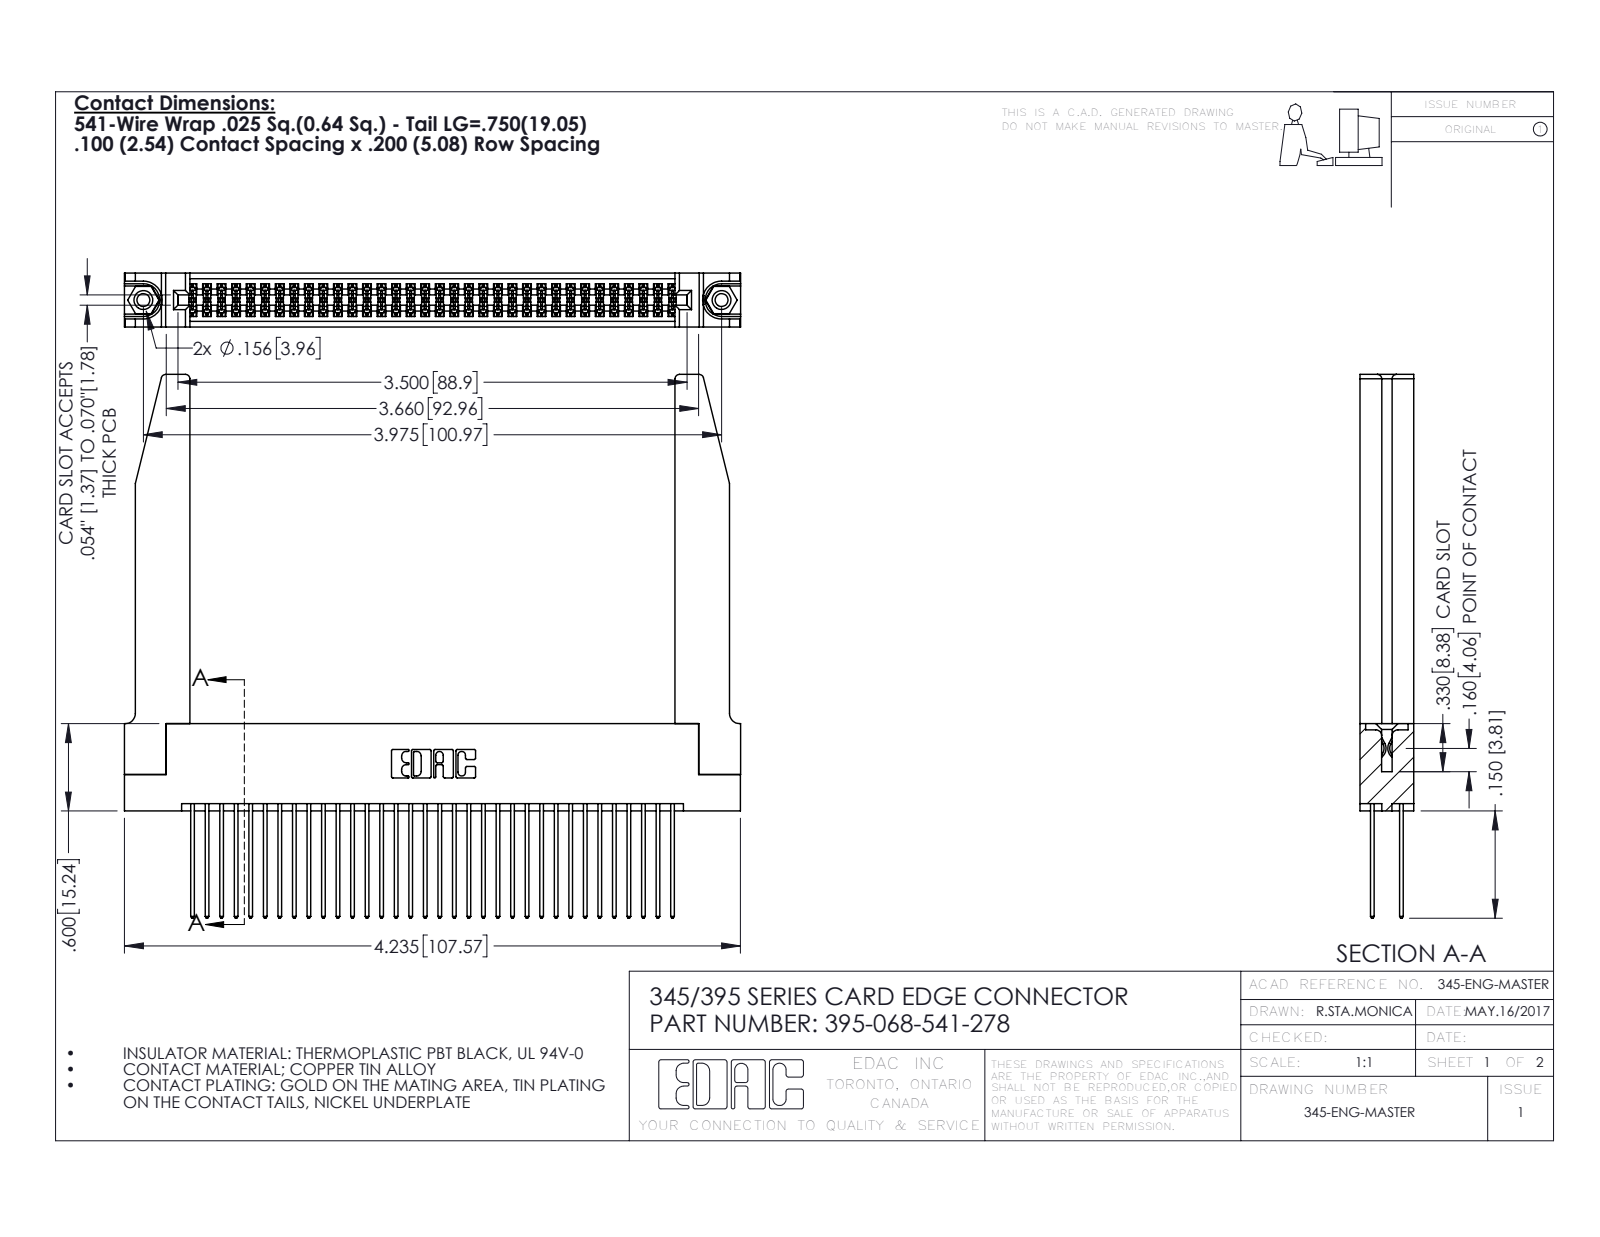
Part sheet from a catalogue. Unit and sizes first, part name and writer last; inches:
Units: inches
Overall size (bounding box): 4.236 × 3.737 × 0.37
Round holes (diameter × count): ⌀0.089 ×2, ⌀0.125 ×2, ⌀0.156 ×2, ⌀0.064 ×1
Round bosses / shafts (diameter × count): ⌀0.155 ×2
Partial cylindrical surfaces — rounded edges, fillets, slot ends (radius × count): R0.006 ×102, R0.01 ×68, R0.01 ×22, R0.03 ×8, R0.007 ×6, R0.031 ×6, R0.026 ×3, R0.014 ×2
Main face-to-face distances: 0.072, 0.298, 0.37, 0.2, 0.098, 0.272, 0.025, 0.225, 0.175, 0.15
Hole centre spacings: 0.27, 3.74, 3.975
Volume: 1.131 in³ · Surface area: 37.87 in²
Bodies: 73 solids, 3760 faces (2466 planar, 1242 cylindrical, 52 other)
Part name (STEP PRODUCT): 345-220-078_345-220-078; 345-292-001_345-293-141; 345-250-001_345-250-001-102; 395-068-541-278 (+1 more)
STEP written by: SolidWorks 2016 (CONFIG_CONTROL_DESIGN)
